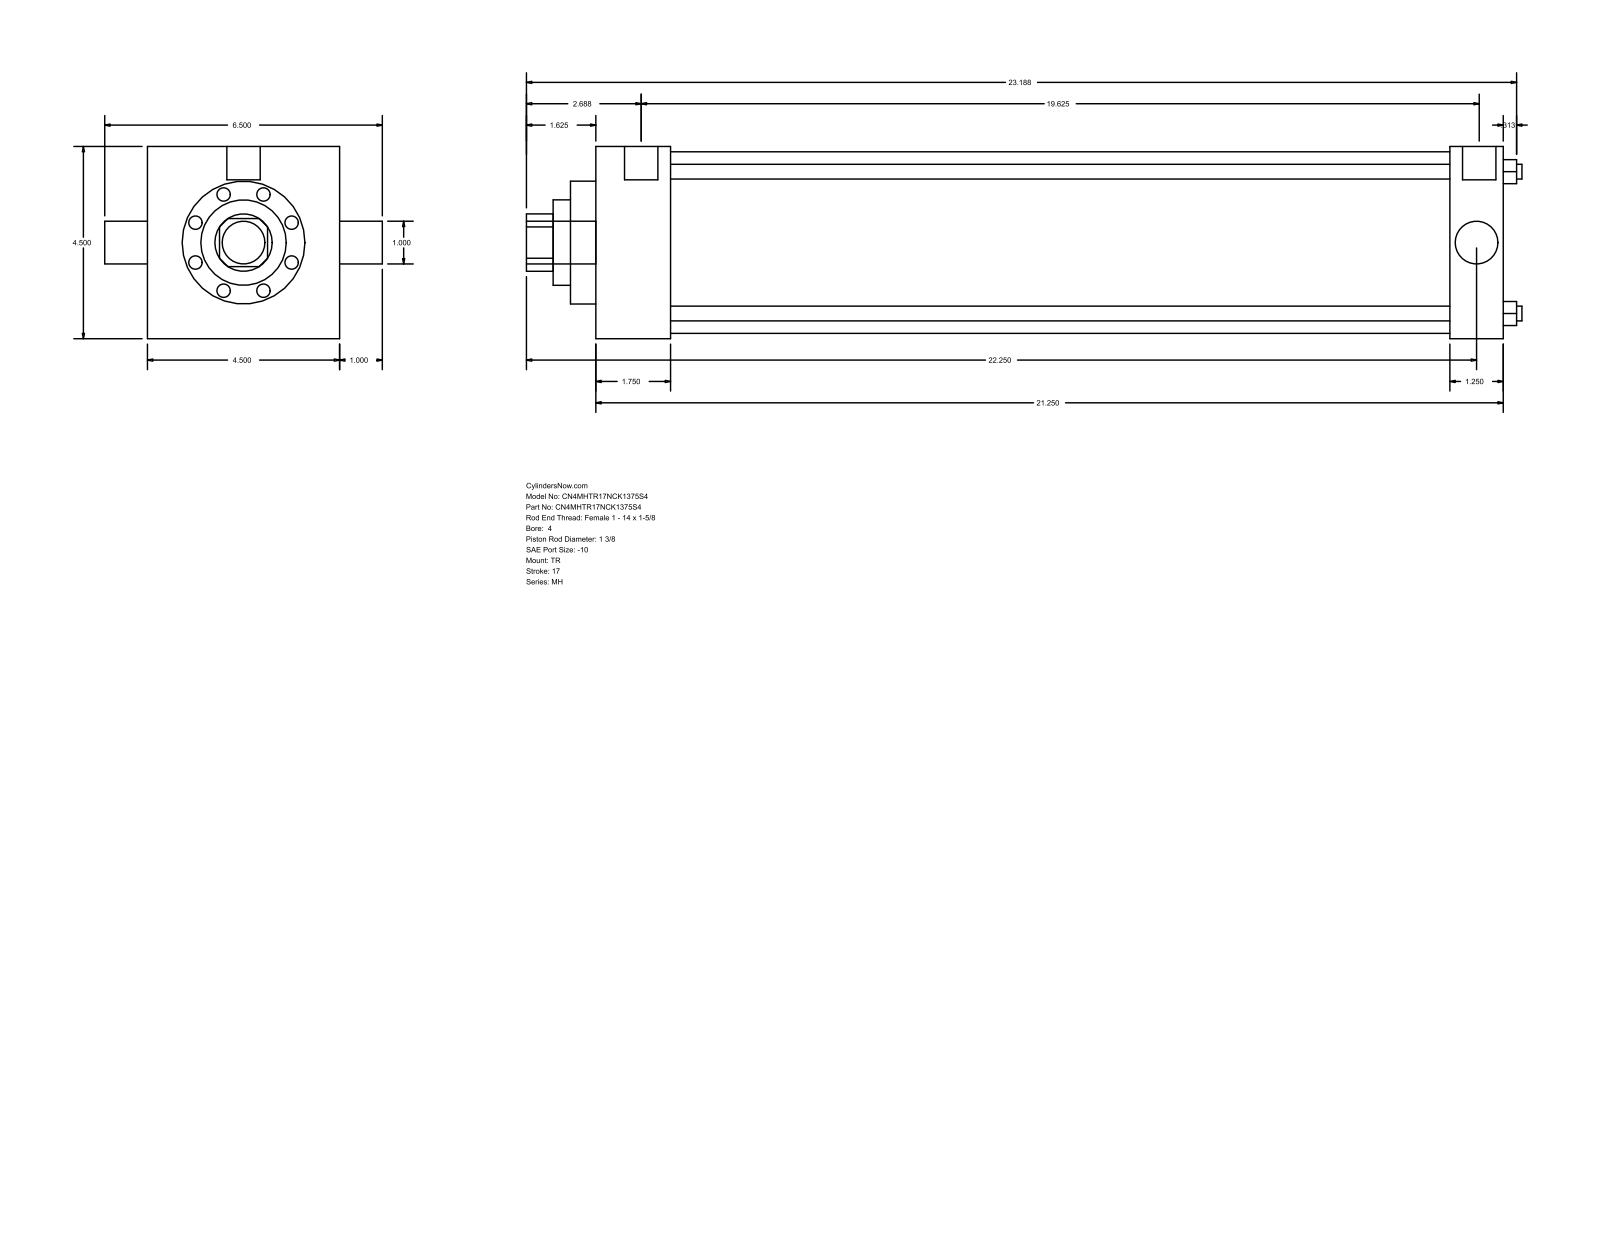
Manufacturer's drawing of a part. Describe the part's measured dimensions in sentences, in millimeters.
The part is named "MH_TR__0400_1.375". Its 3-D file was written by "GSSL Pune (CONFIG_CONTROL_DESIGN)". It is 0 solids with 86 faces: 61 planar, 25 cylindrical and 0 other. Overall it measures 592.14 by 165.1 by 114.3 millimeters. Round holes: 4 of diameter 8.76, 1 of diameter 25.4, 1 of diameter 34.92, 1 of diameter 50.8, 1 of diameter 73.03, 1 of diameter 107.95. Round bosses or shafts: 3 of diameter 8.73, 2 of diameter 19.84, 1 of diameter 25.4. Partial cylindrical surfaces (rounded edges, fillets, slot ends): 1 of radius 17.06. The main face-to-face distances are 114.3, 539.75, 44.45, 495.3, 508, 463.55, 31.75, 15.08, 59.53, 523.08. The hole center spacings are 59.62, 84.32, 119.25.
